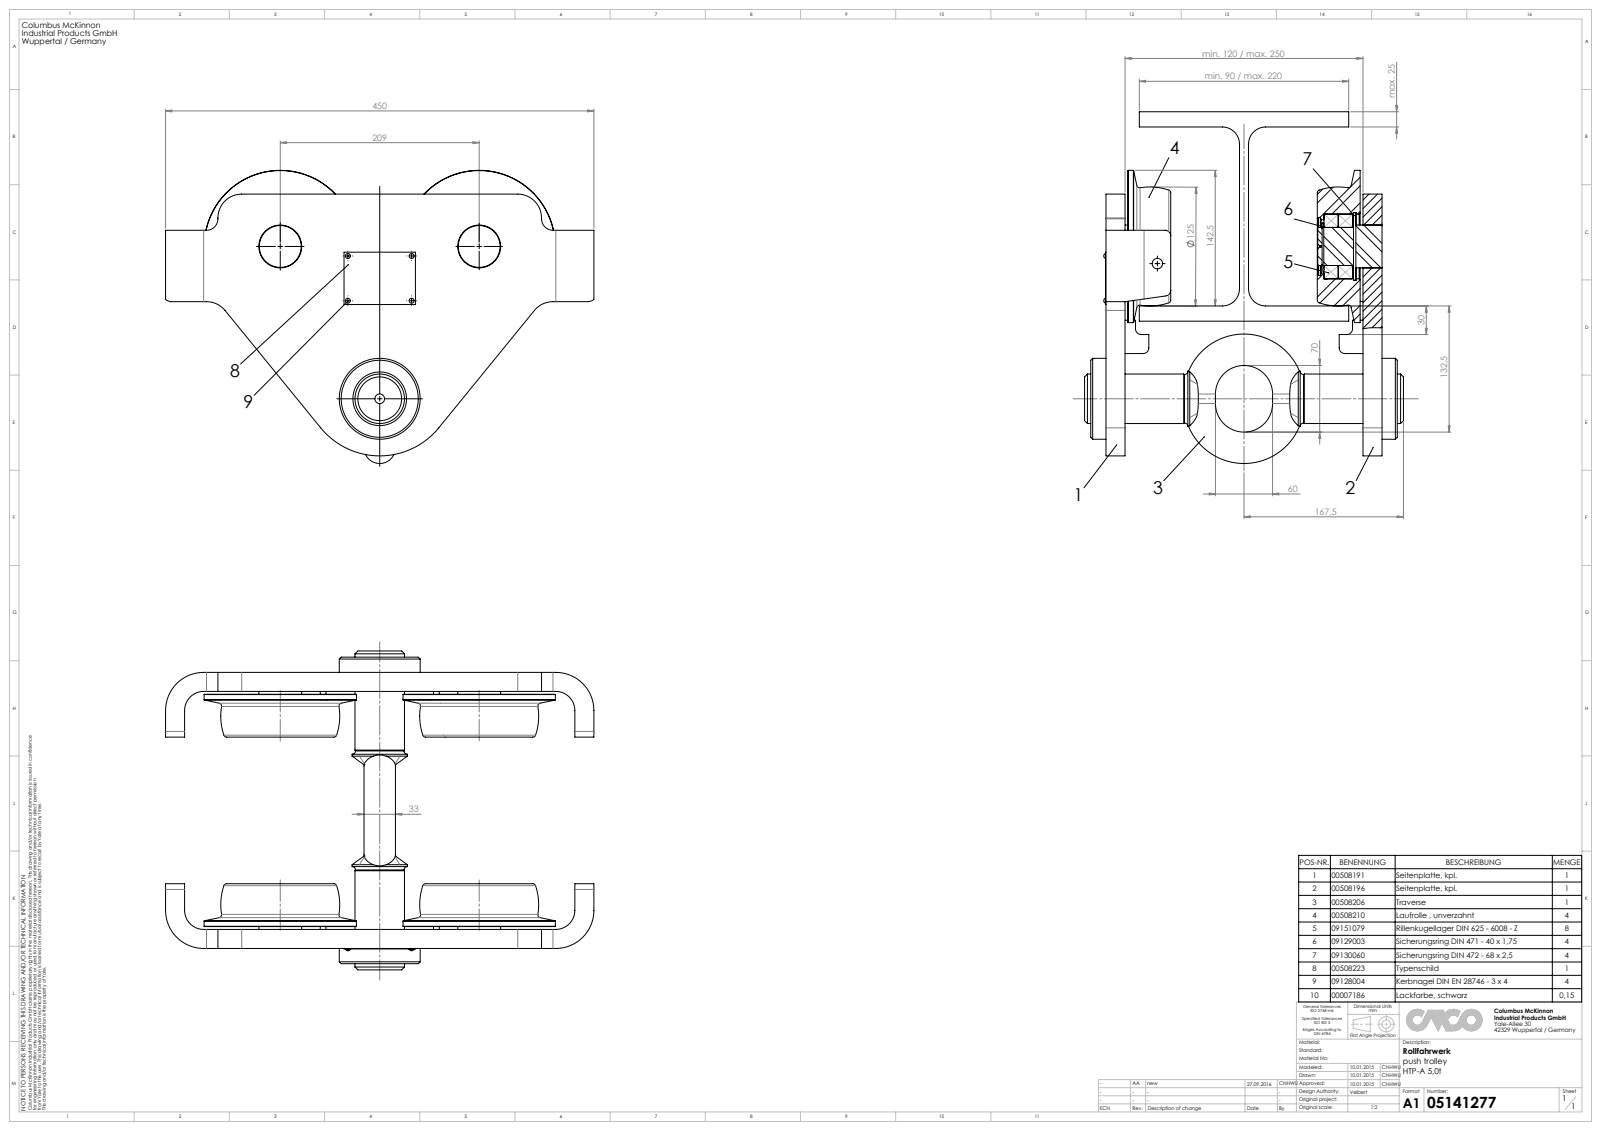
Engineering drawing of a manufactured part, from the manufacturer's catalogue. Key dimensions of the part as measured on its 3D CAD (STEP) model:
Part name (STEP PRODUCT): HTP-A 5,0t
STEP written by: SolidWorks 2015 (AUTOMOTIVE_DESIGN)
Units: millimetres
Bodies: 39 solids, 862 faces (246 planar, 364 cylindrical, 252 other)
Overall size (bounding box): 500 × 369.5 × 335
Volume: 11 040 000 mm³ · Surface area: 1 566 000 mm²
Round holes (diameter × count): ⌀3 ×10, ⌀2.5 ×8, ⌀3.5 ×4, ⌀2 ×2, ⌀11 ×2, ⌀37.5 ×2, ⌀40 ×2, ⌀45 ×2, ⌀55.4 ×2, ⌀56 ×2, ⌀58 ×2, ⌀61 ×2
Round bosses / shafts (diameter × count): ⌀5.2 ×4, ⌀160 ×2, ⌀71 ×2, ⌀49.49 ×2, ⌀85 ×1, ⌀69 ×1, ⌀58 ×1, ⌀52 ×1
Partial cylindrical surfaces — rounded edges, fillets, slot ends (radius × count): R2.5 ×8, R6 ×8, R3 ×6, R18 ×4, R20 ×4, R25 ×4, R40 ×4, R12 ×2
Main face-to-face distances: 16, 204, 140.25, 149.75, 20, 270, 120.25, 129.75, 220, 188
Hole centre spacings: 209, 6.25, 9.87, 12.01, 21.74, 21.75, 30.76, 31.59
